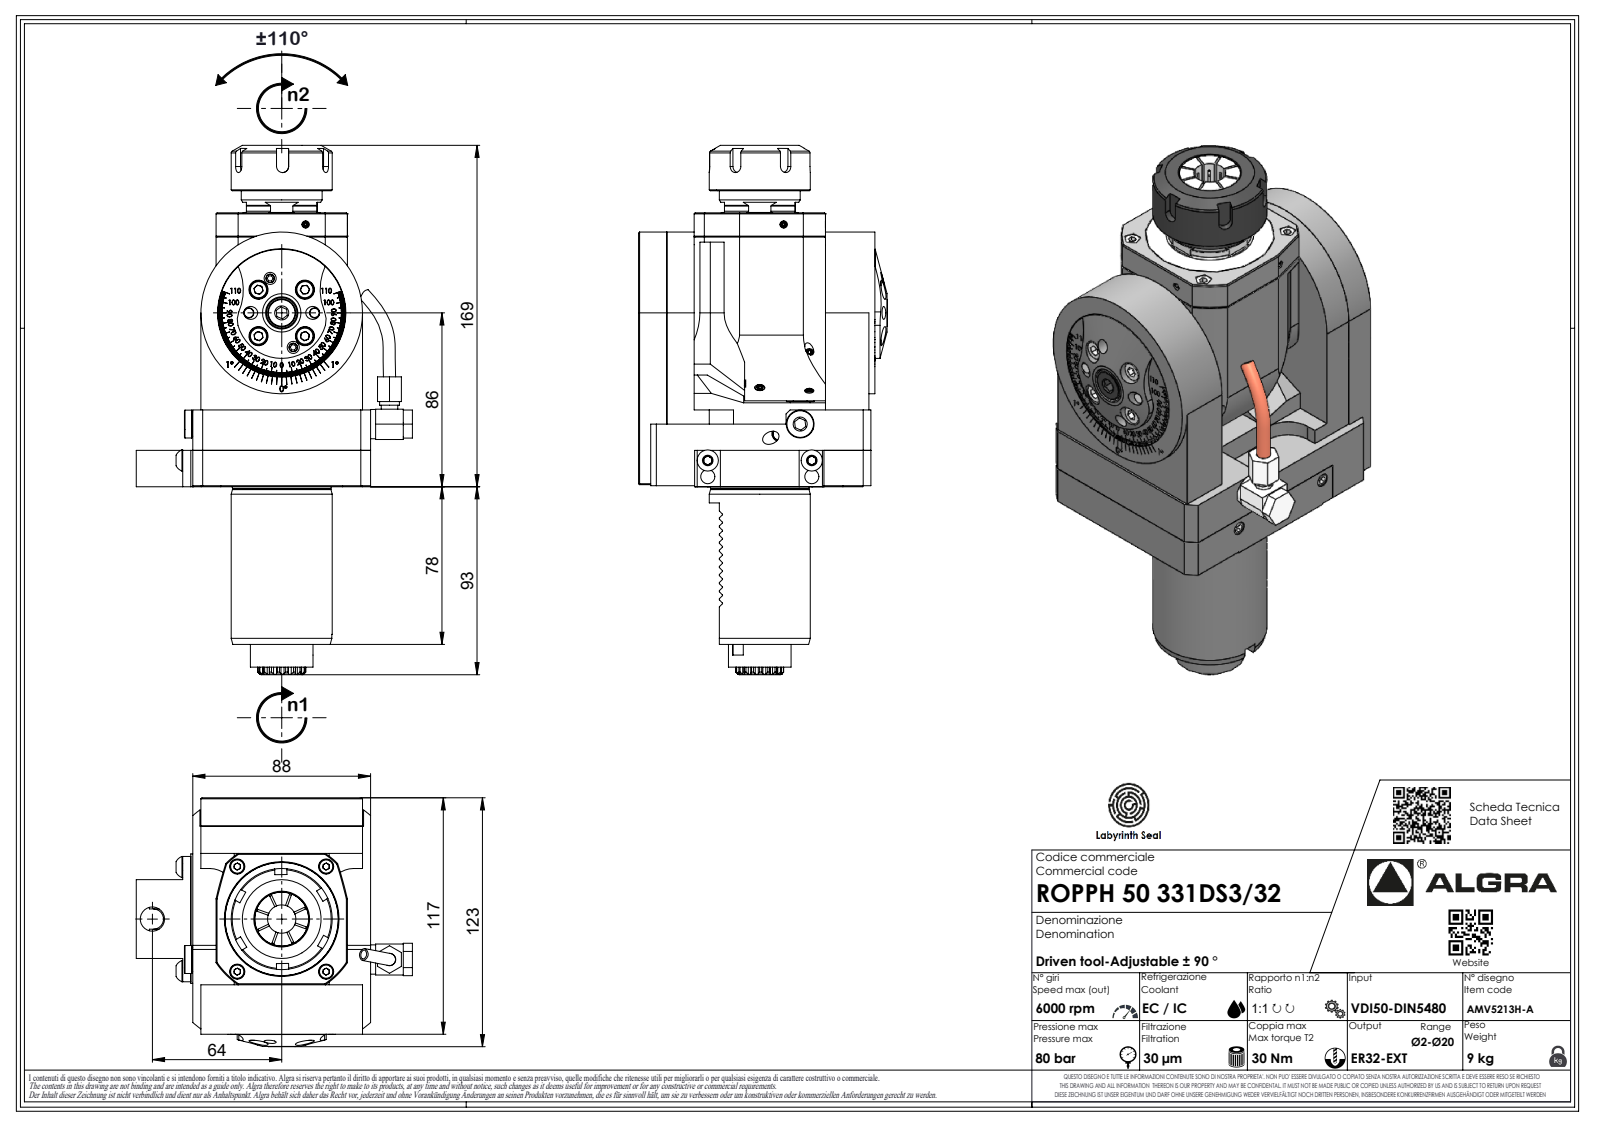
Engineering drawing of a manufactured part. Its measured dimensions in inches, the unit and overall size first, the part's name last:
Units: inches
Overall size (bounding box): 10.311 × 5.382 × 4.843
Round holes (diameter × count): ⌀0.083 ×1, ⌀1.417 ×1
Round bosses / shafts (diameter × count): ⌀3.15 ×1, ⌀1.969 ×1, ⌀1.917 ×1, ⌀1.575 ×1, ⌀1.377 ×1, ⌀1.22 ×1, ⌀0.571 ×1, ⌀0.386 ×1
Partial cylindrical surfaces — rounded edges, fillets, slot ends (radius × count): R0.063 ×36, R0.012 ×12, R0.013 ×7, R0.02 ×7, R0.146 ×7, R0.118 ×5, R0.394 ×2, R0.472 ×2
Main face-to-face distances: 0.157, 2.559, 3.307, 0.453, 0.02, 2.854, 3.012, 0.295, 1.083, 3.524
Volume: 78.05 in³ · Surface area: 175.3 in²
Bodies: 1 solid, 757 faces (424 planar, 147 cylindrical, 186 other)
Part name (STEP PRODUCT): ROPPH50331DS332
STEP written by: SolidWorks 2023 (AUTOMOTIVE_DESIGN)
